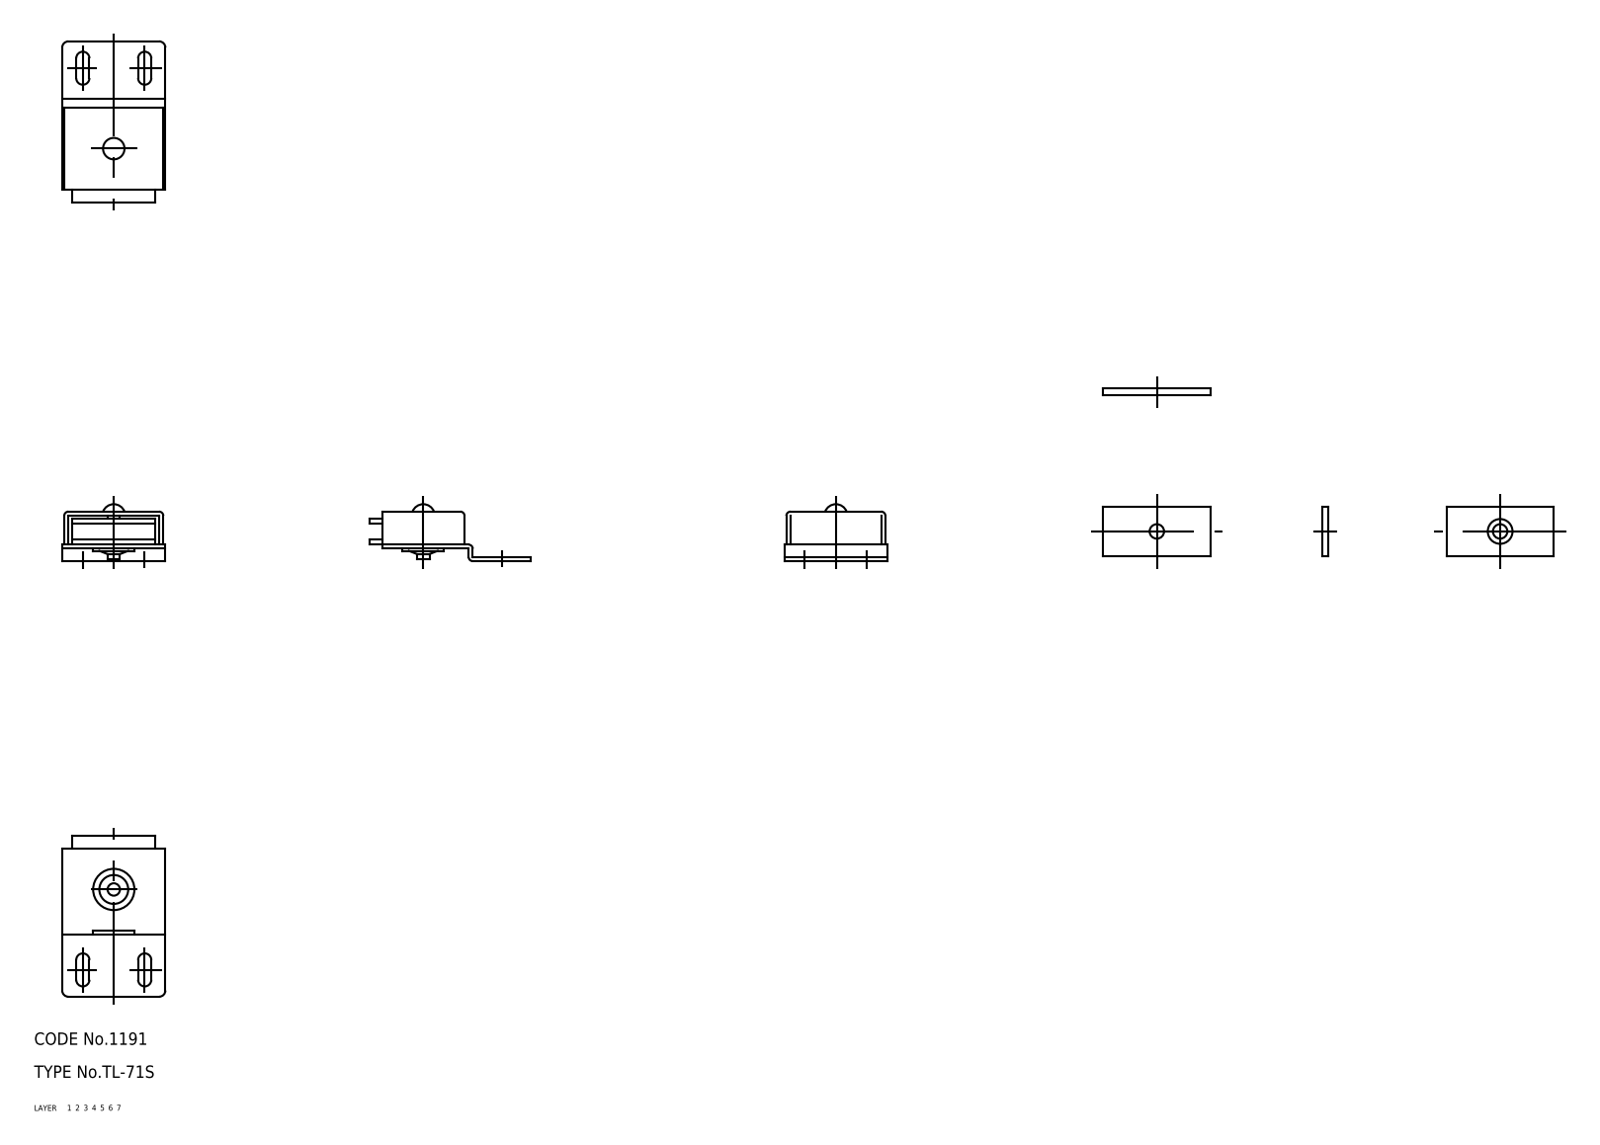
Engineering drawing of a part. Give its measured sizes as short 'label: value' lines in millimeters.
name: 67113382; 67113395; 67113408; 67113421 (+4 more)
written by: CADfix (AUTOMOTIVE_DESIGN)
unit: mm
bodies: 8 solids, 102 faces (0 planar, 0 cylindrical, 102 other)
size: 60.6 × 26 × 13.8
volume: 4 673 mm³; area: 7 664 mm²
